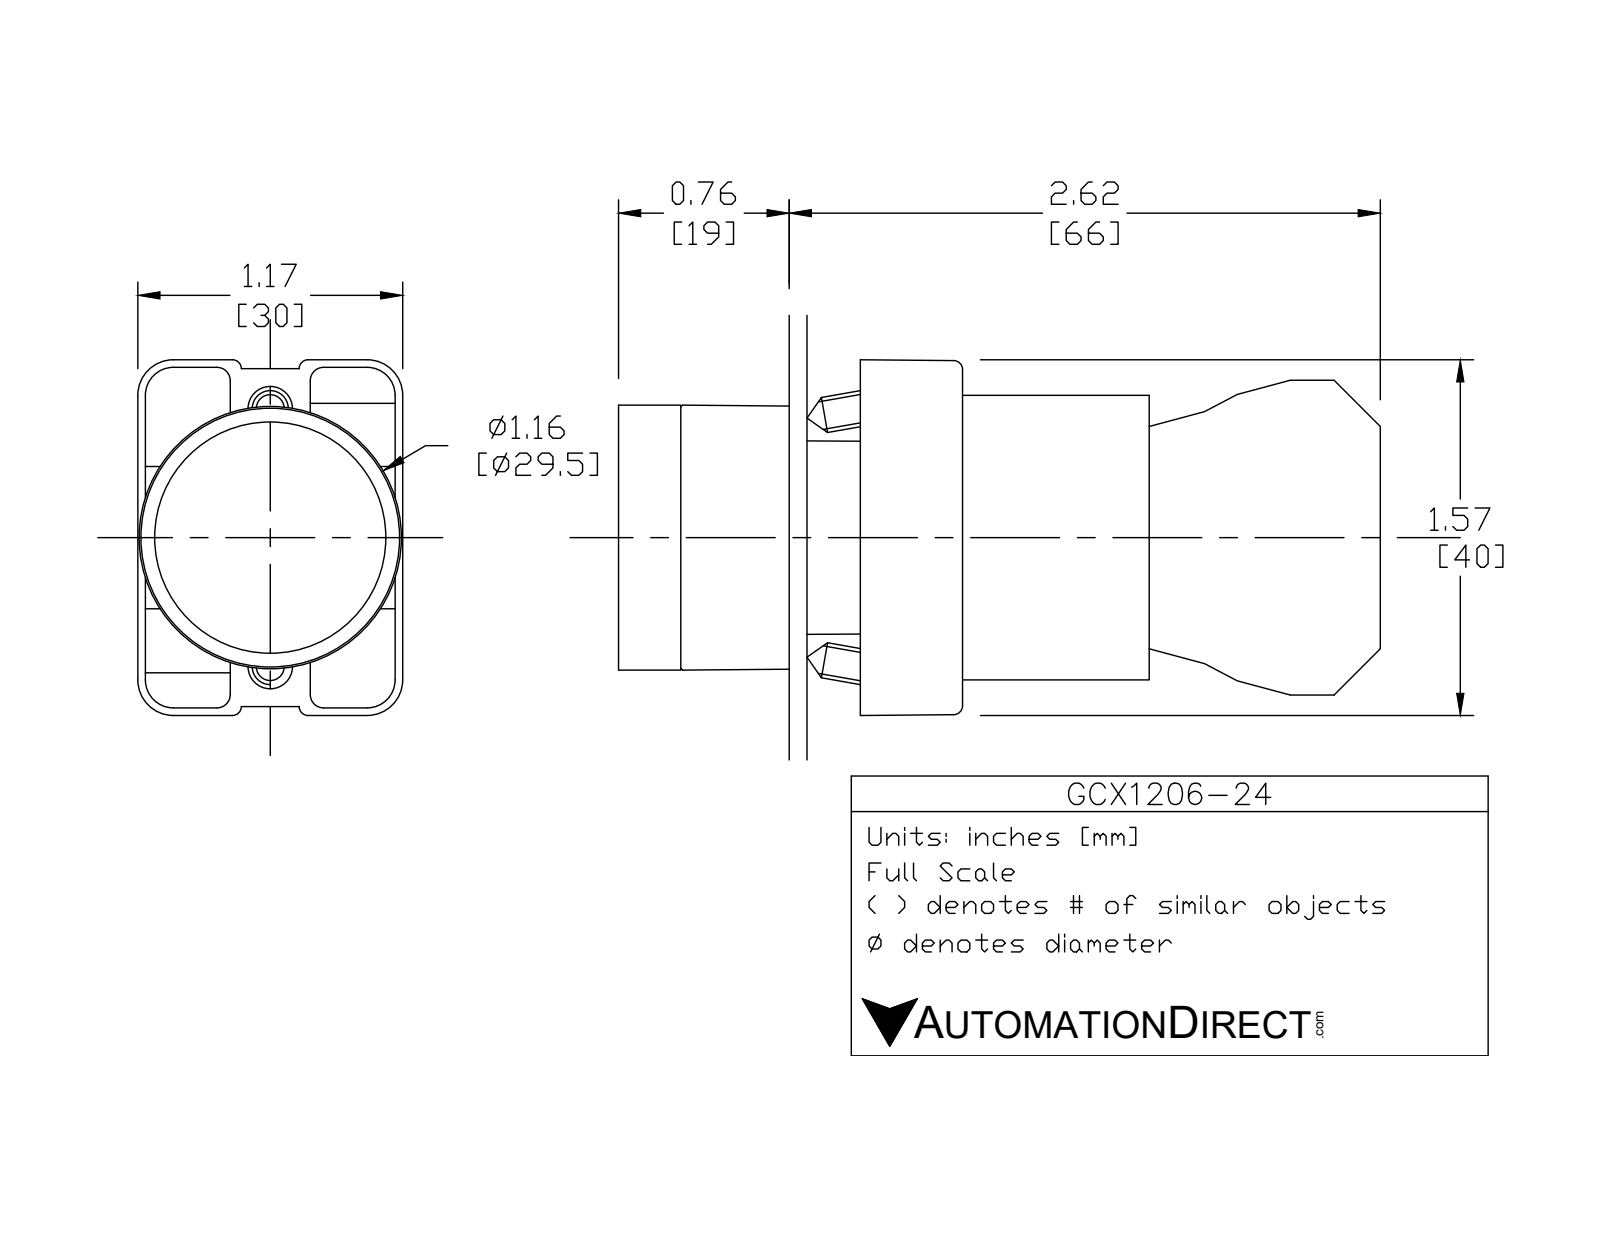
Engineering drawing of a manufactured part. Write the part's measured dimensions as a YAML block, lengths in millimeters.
part_name: "GCX1206-24; ECX1050; ecx1040; ecx1029 (+1 more)"
step_written_by: "SolidWorks 2016 (AUTOMOTIVE_DESIGN)"
units: millimeters
bodies: {solids: 8, faces: 431, planar: 252, cylindrical: 148, other: 31}
overall_size: [84.3, 40.2, 29.9]
volume: 45790
surface_area: 25000
round_holes:
  - {diameter: 2, count: 2}
  - {diameter: 3.1, count: 2}
  - {diameter: 3.3, count: 2}
  - {diameter: 2.2, count: 1}
  - {diameter: 5, count: 1}
  - {diameter: 11.9, count: 1}
  - {diameter: 22.3, count: 1}
  - {diameter: 22.6, count: 1}
  - {diameter: 26, count: 1}
round_bosses_or_shafts:
  - {diameter: 4, count: 4}
  - {diameter: 29.8, count: 1}
  - {diameter: 25.5, count: 1}
  - {diameter: 24, count: 1}
  - {diameter: 21.7, count: 1}
  - {diameter: 19.8, count: 1}
  - {diameter: 12.8, count: 1}
partial_cylinders:
  - {radius: 1.5, count: 24}
  - {radius: 1, count: 12}
  - {radius: 3.1, count: 12}
  - {radius: 4, count: 12}
  - {radius: 1, count: 8}
  - {radius: 3.3, count: 2}
  - {radius: 0.5, count: 1}
  - {radius: 1.6, count: 1}
face_to_face_distances: [21, 51.3, 30.3, 14.7, 29.7, 0.8, 7, 0.8, 19, 14.6]
hole_center_spacings: [6, 13.8, 12, 12.4]
